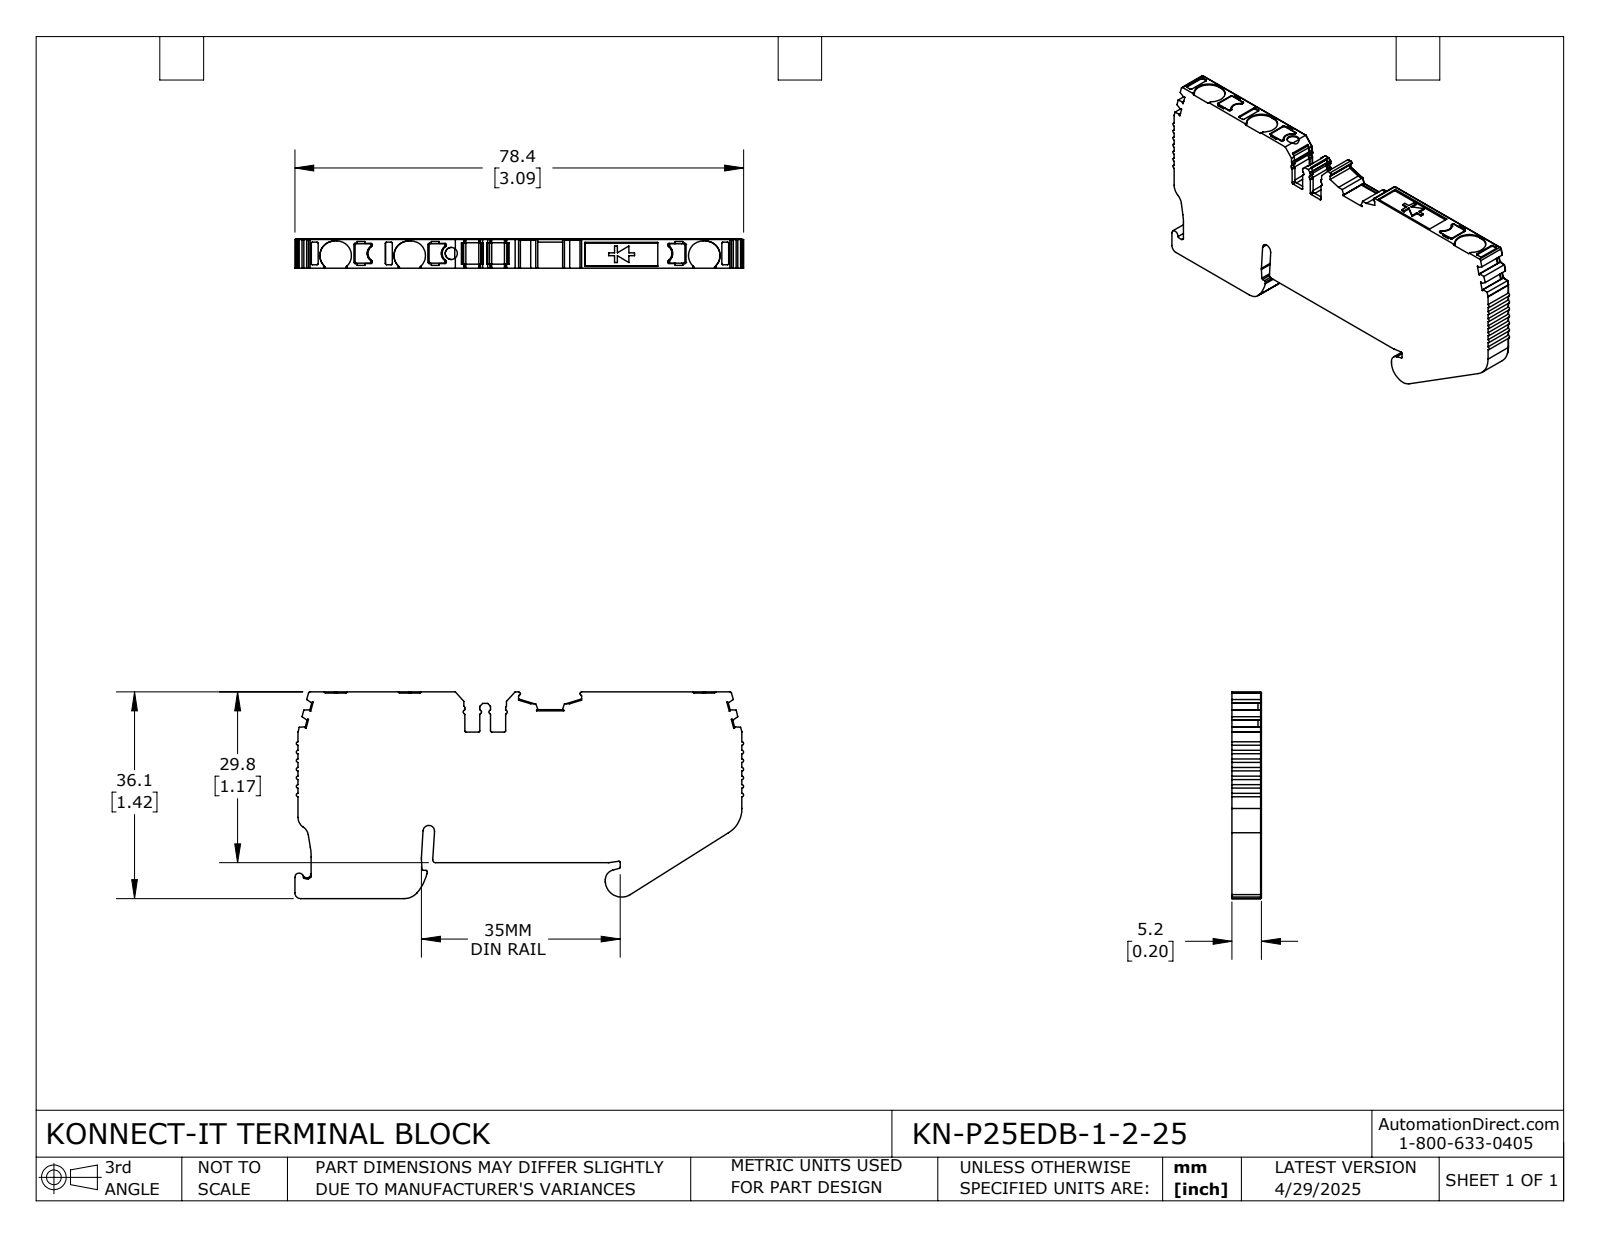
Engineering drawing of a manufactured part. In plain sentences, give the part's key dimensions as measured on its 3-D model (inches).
The part is named "KN-P25EDB-1-2-25". Its 3-D file was written by "SolidWorks 2024 (CONFIG_CONTROL_DESIGN)". It is 1 solid with 595 faces: 341 planar, 251 cylindrical and 3 other. Overall it measures 3.085 by 1.42 by 0.203 inches. Its volume is 0.731 cubic inches and its surface area 9.629 square inches. Round holes: 1 of diameter 0.083. Partial cylindrical surfaces (rounded edges, fillets, slot ends): 66 of radius 0.008, 39 of radius 0.012, 16 of radius 0.02, 13 of radius 0.004, 12 of radius 0.006, 9 of radius 0.016, 6 of radius 0.1, 3 of radius 0.039. The main face-to-face distances are 0.203, 1.166, 1.174, 0.246, 1.412, 1.42, 3.052, 0.047, 0.197, 0.177.
